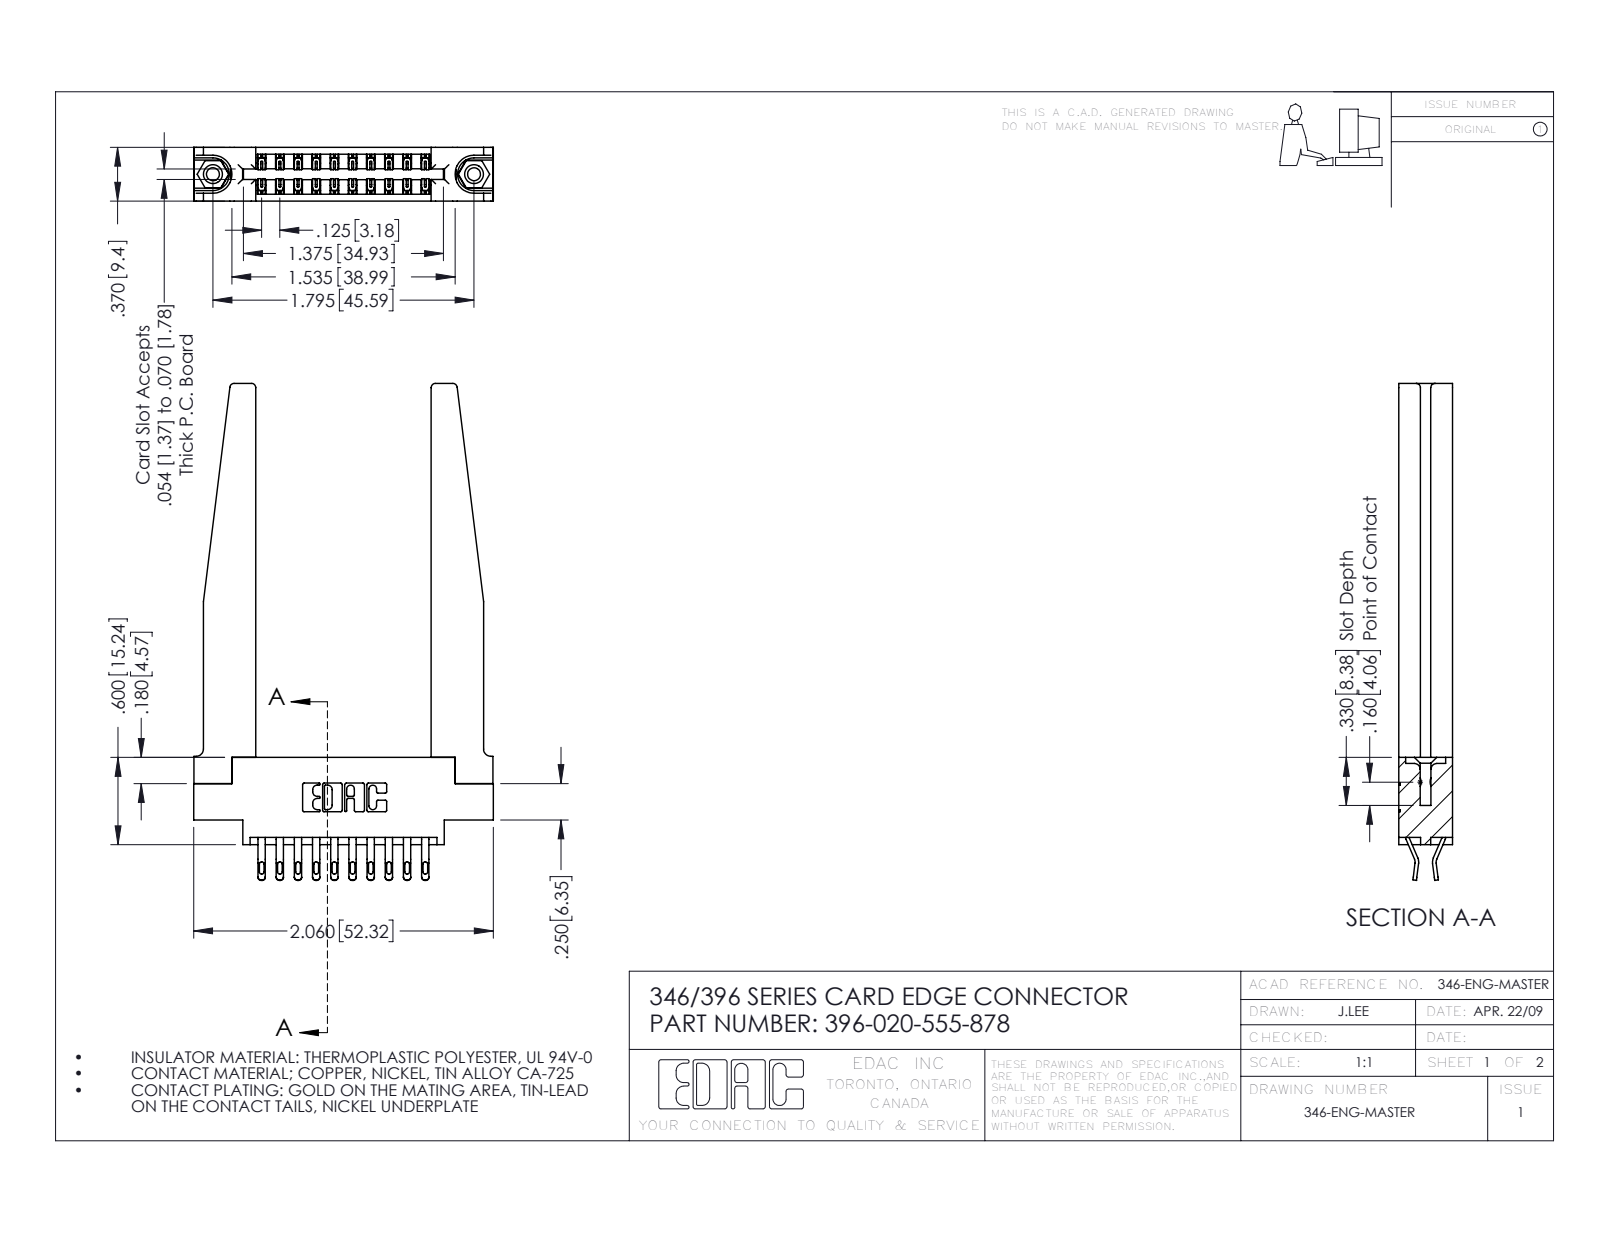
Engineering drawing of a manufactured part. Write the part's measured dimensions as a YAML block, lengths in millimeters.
part_name: "346-220-078_345-220-078; 345-250-001_345-250-001-102; 396-020-555-878; 346 Part_0.170 Offset - 0.156 Dia-TH (+1 more)"
step_written_by: "SolidWorks 2016 (CONFIG_CONTROL_DESIGN)"
units: millimeters
bodies: {solids: 25, faces: 1520, planar: 882, cylindrical: 586, other: 52}
overall_size: [86.7, 52.3, 9.4]
volume: 11700
surface_area: 12960
round_holes:
  - {diameter: 2.3, count: 2}
  - {diameter: 3.2, count: 2}
  - {diameter: 4, count: 2}
  - {diameter: 1.6, count: 1}
round_bosses_or_shafts:
  - {diameter: 3.9, count: 2}
partial_cylinders:
  - {radius: 0.4, count: 40}
  - {radius: 0.5, count: 40}
  - {radius: 0.2, count: 30}
  - {radius: 0.3, count: 22}
  - {radius: 0.8, count: 8}
  - {radius: 0.2, count: 6}
  - {radius: 0.8, count: 6}
  - {radius: 1.3, count: 4}
face_to_face_distances: [9.4, 3.8, 3.8, 1.8, 1.2, 8.2, 2.6, 5.6, 4.4, 6.4]
hole_center_spacings: [6.2, 40.4, 45.6]
